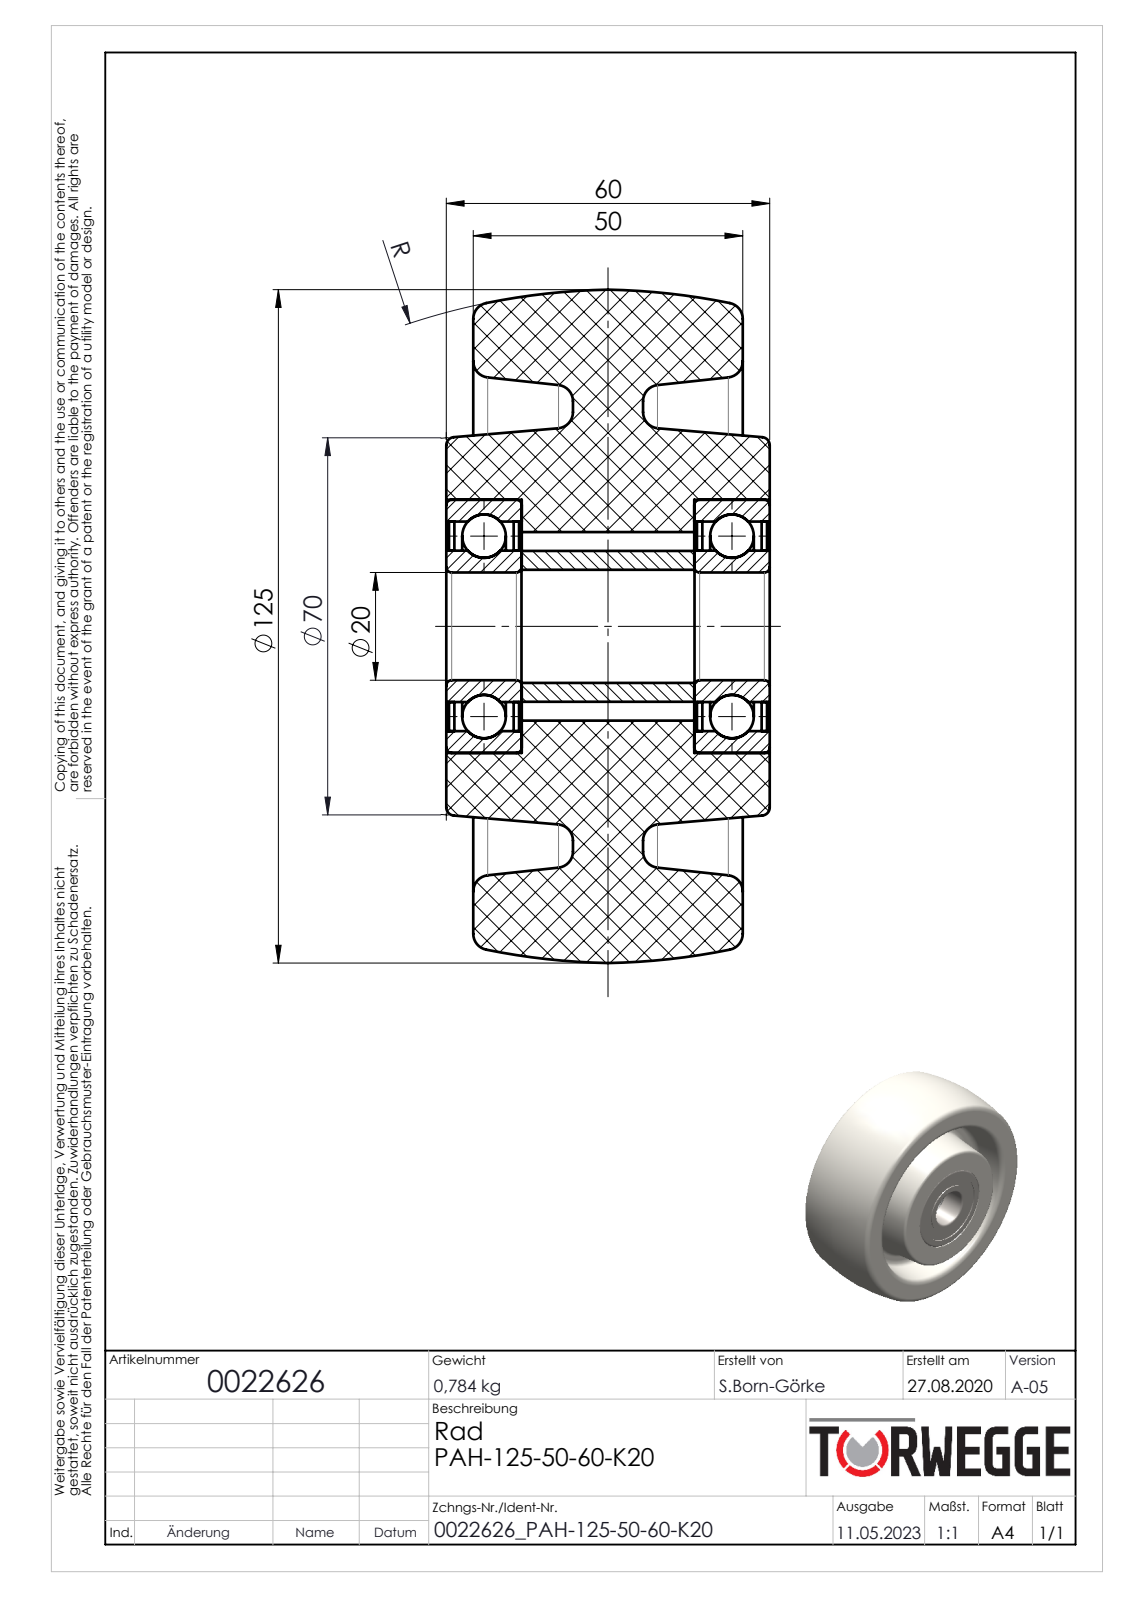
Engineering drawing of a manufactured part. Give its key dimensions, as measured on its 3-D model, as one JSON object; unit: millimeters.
{"part_name": "0022626", "step_written_by": "SolidWorks 2020 (AUTOMOTIVE_DESIGN)", "units": "millimeters", "bodies": {"solids": 14, "faces": 156, "planar": 34, "cylindrical": 54, "other": 68}, "overall_size": [125, 125, 60], "volume_mm3": 507100, "surface_area_mm2": 95659, "round_holes": [[20, 1], [21, 1], [28.1, 1], [35, 1], [38.9, 1], [47, 1]], "round_bosses_or_shafts": [[28, 1]], "partial_cylinders_radius": [[16.07, 1], [17.43, 1]], "face_to_face_distances": [46, 5, 55, 14, 9, 41, 50, 60, 0.5, 1.5]}
